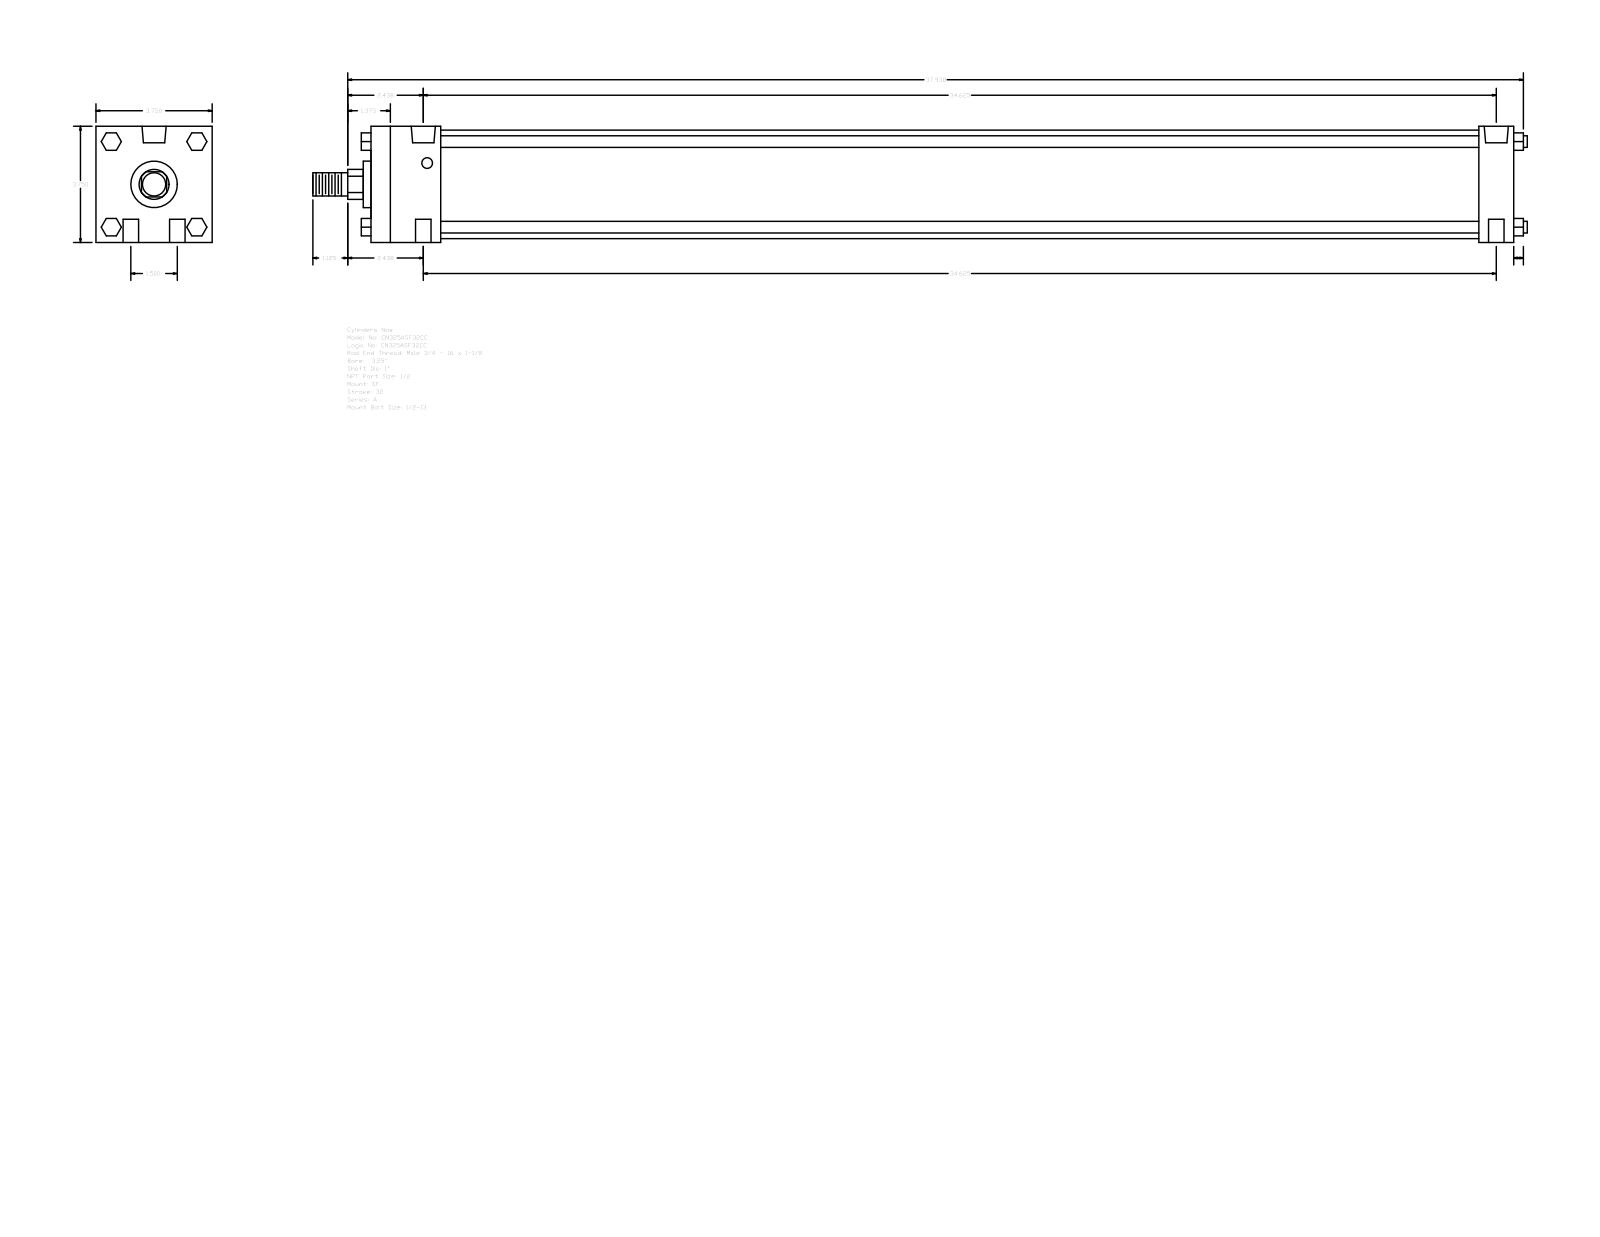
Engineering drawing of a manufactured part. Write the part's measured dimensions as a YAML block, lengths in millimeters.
part_name: "A_SF__0325_1"
step_written_by: "GSSL Pune (CONFIG_CONTROL_DESIGN)"
units: millimeters
bodies: {solids: 0, faces: 124, planar: 94, cylindrical: 30, other: 0}
overall_size: [995.36, 95.25, 95.25]
round_holes:
  - {diameter: 12.7, count: 4}
  - {diameter: 8.73, count: 2}
  - {diameter: 19.77, count: 2}
round_bosses_or_shafts:
  - {diameter: 9.53, count: 4}
  - {diameter: 88.9, count: 1}
  - {diameter: 38.1, count: 1}
  - {diameter: 25.4, count: 1}
  - {diameter: 19.05, count: 1}
partial_cylinders:
  - {radius: 12.29, count: 1}
face_to_face_distances: [95.24, 936.62, 28.57, 908.05, 57.15, 850.9, 879.47, 14.28, 35.05, 60.71]
hole_center_spacings: [19.05, 879.69, 879.48, 38.1, 880.3, 873.12]
